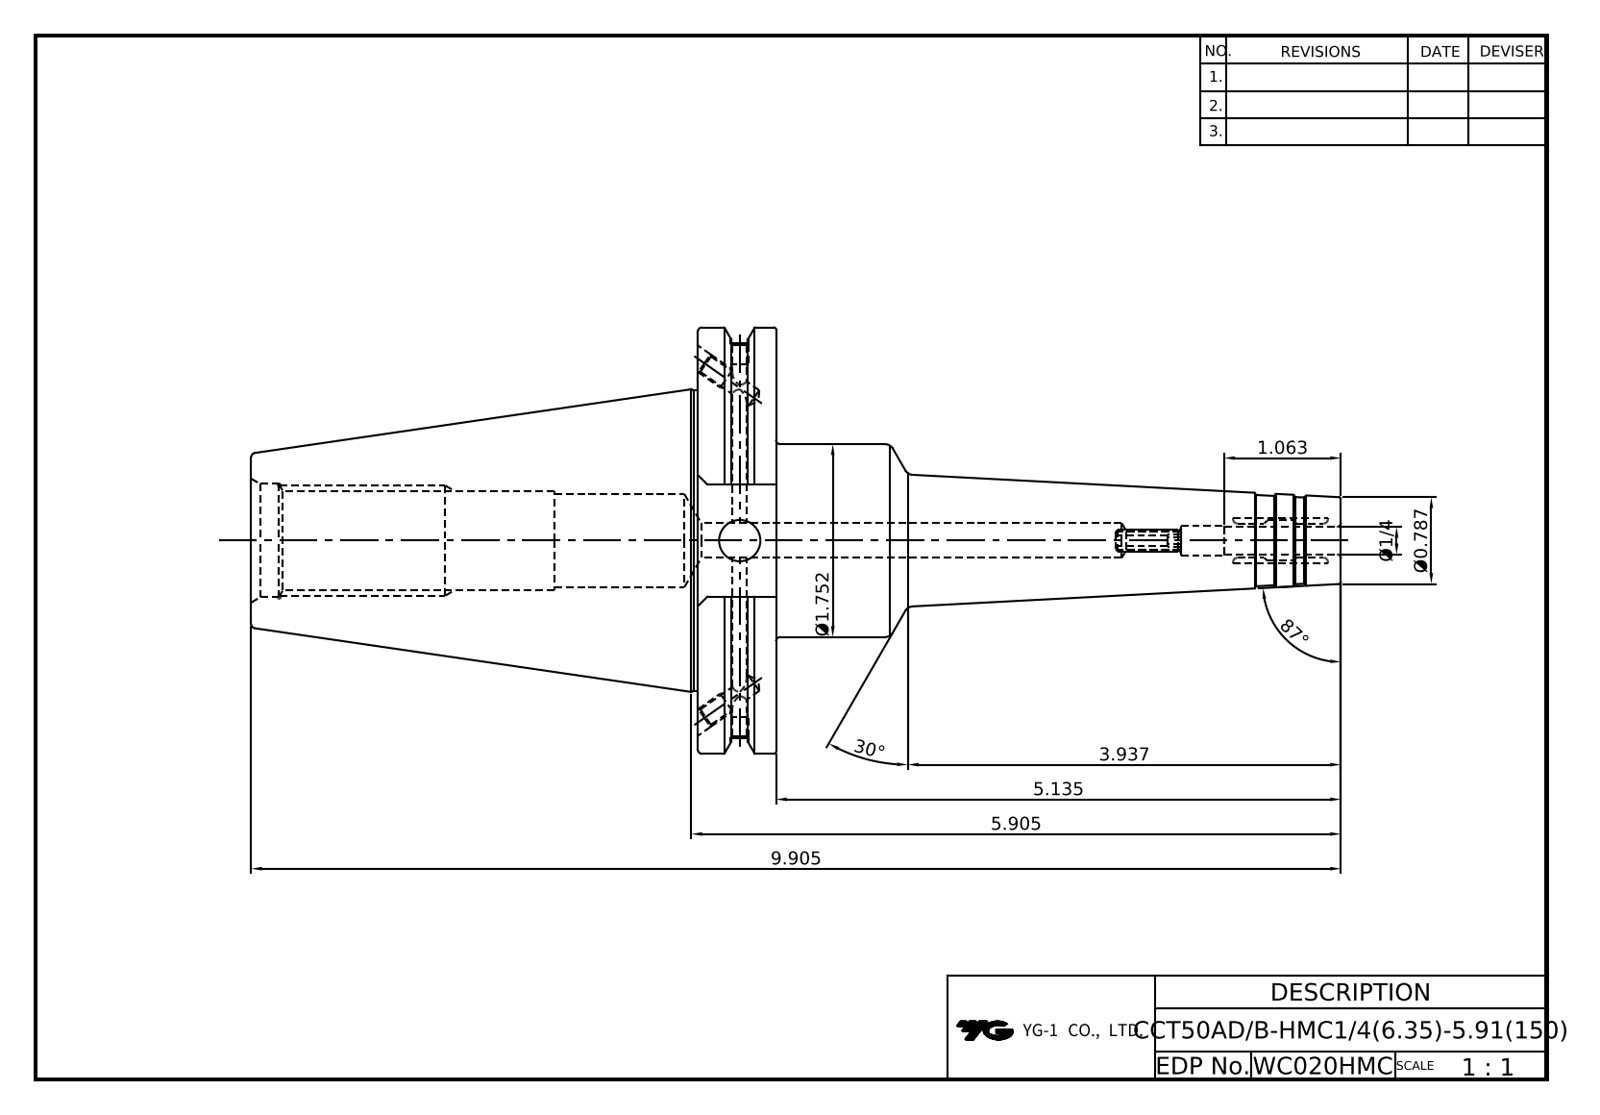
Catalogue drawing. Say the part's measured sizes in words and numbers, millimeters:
The part is named "LO-CCT50ADB-HMC6.35-150". Its 3-D file was written by "Autodesk Inventor 2024 (AUTOMOTIVE_DESIGN)". It is 1 solid with 106 faces: 38 planar, 27 cylindrical and 41 other. Overall it measures 251.6 by 98.42 by 94.69 millimeters. Its volume is 420 868 cubic millimeters and its surface area 59 081 square millimeters. Round holes: 2 of diameter 3.24, 2 of diameter 4.13, 2 of diameter 4.2, 2 of diameter 5, 1 of diameter 4.3, 1 of diameter 6.35, 1 of diameter 6.8, 1 of diameter 8, 1 of diameter 9.53, 1 of diameter 21.97, 1 of diameter 26.2. Round bosses or shafts: 1 of diameter 98.42, 1 of diameter 91.29, 1 of diameter 69.25, 1 of diameter 44.5. The main face-to-face distances are 17.55, 103.1, 120.65, 73.03, 25.9, 251.6, 148.5, 130.95, 103.5, 0.4.
